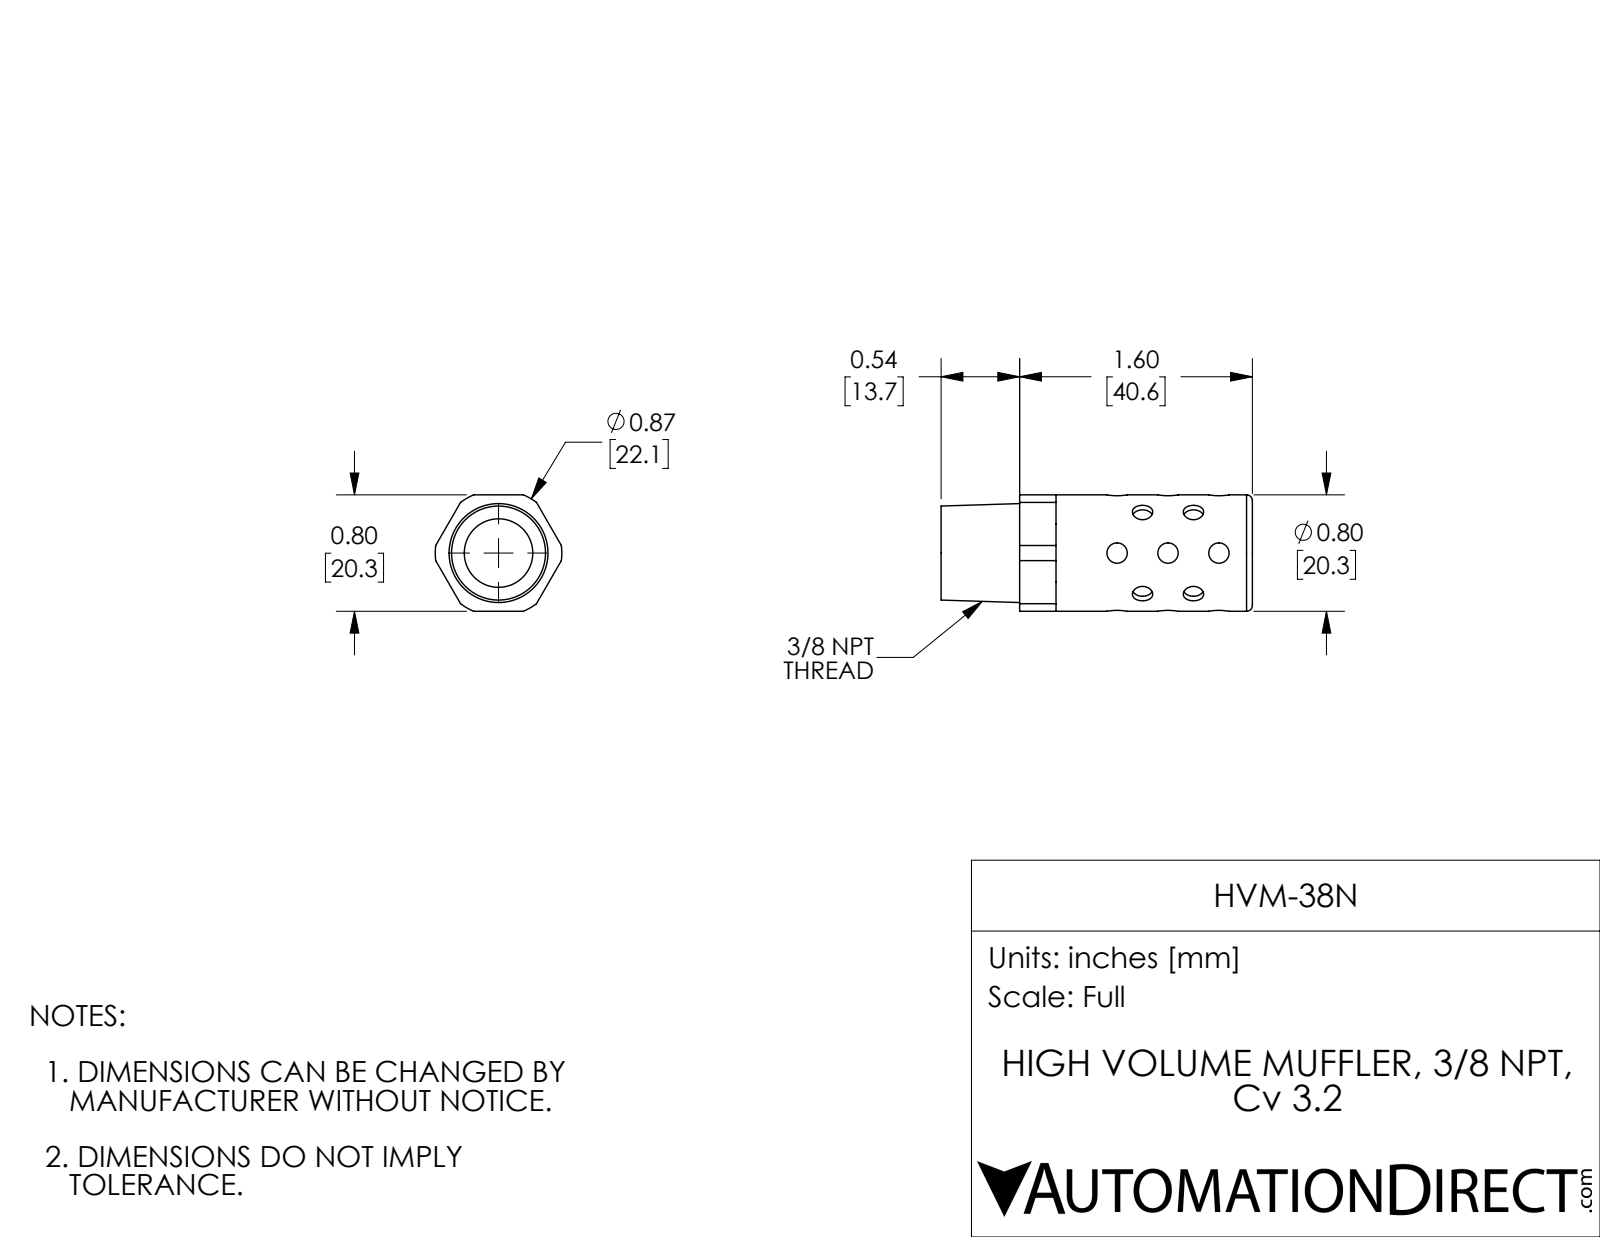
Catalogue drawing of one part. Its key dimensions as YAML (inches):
part_name: "HVM-38N"
step_written_by: "SolidWorks 2017 (AUTOMOTIVE_DESIGN)"
units: inches
bodies: {solids: 1, faces: 91, planar: 36, cylindrical: 51, other: 4}
overall_size: [2.14, 0.87, 0.8]
volume: 0.657
surface_area: 9.409
round_holes:
  - {diameter: 0.14, count: 10}
  - {diameter: 0.471, count: 1}
round_bosses_or_shafts:
  - {diameter: 0.8, count: 1}
partial_cylinders:
  - {radius: 0.435, count: 1}
face_to_face_distances: [0.8, 0.25, 1.35, 1.6, 0.7, 0.54, 1.89, 2.14, 0.05, 0.75]
hole_center_spacings: [0.35, 0.7]
